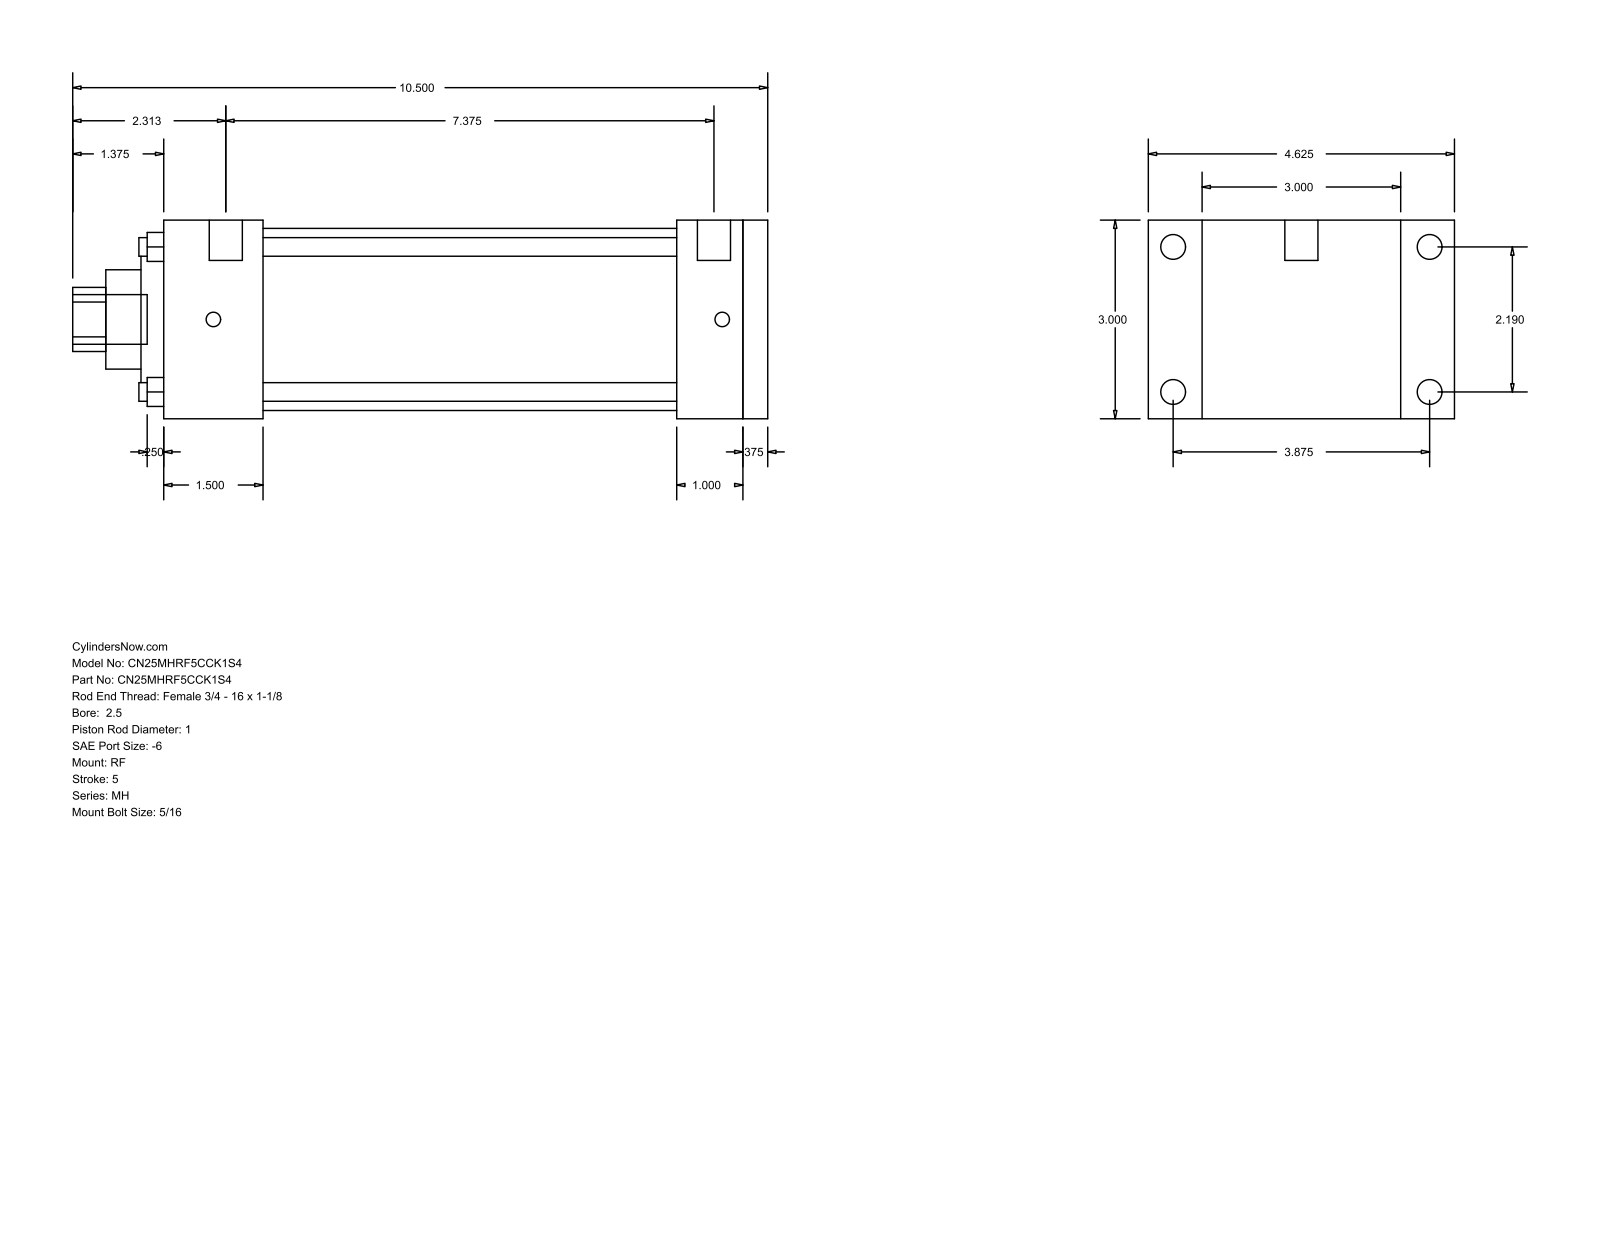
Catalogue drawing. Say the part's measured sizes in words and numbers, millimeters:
The part is named "MH_RF__0250_1". Its 3-D file was written by "GSSL Pune (CONFIG_CONTROL_DESIGN)". It is 0 solids with 94 faces: 65 planar, 29 cylindrical and 0 other. Overall it measures 266.7 by 117.47 by 76.2 millimeters. Round holes: 4 of diameter 7.14, 1 of diameter 25.4, 1 of diameter 38.1, 1 of diameter 60.33, 1 of diameter 69.85. Round bosses or shafts: 4 of diameter 9.53, 4 of diameter 5.56, 2 of diameter 12.7, 1 of diameter 19.05. Partial cylindrical surfaces (rounded edges, fillets, slot ends): 1 of radius 12.29. The main face-to-face distances are 76.2, 9.52, 231.78, 222.26, 25.4, 34.92, 196.86, 38.11, 158.75, 184.15. The hole center spacings are 39.33, 55.62, 78.66.
